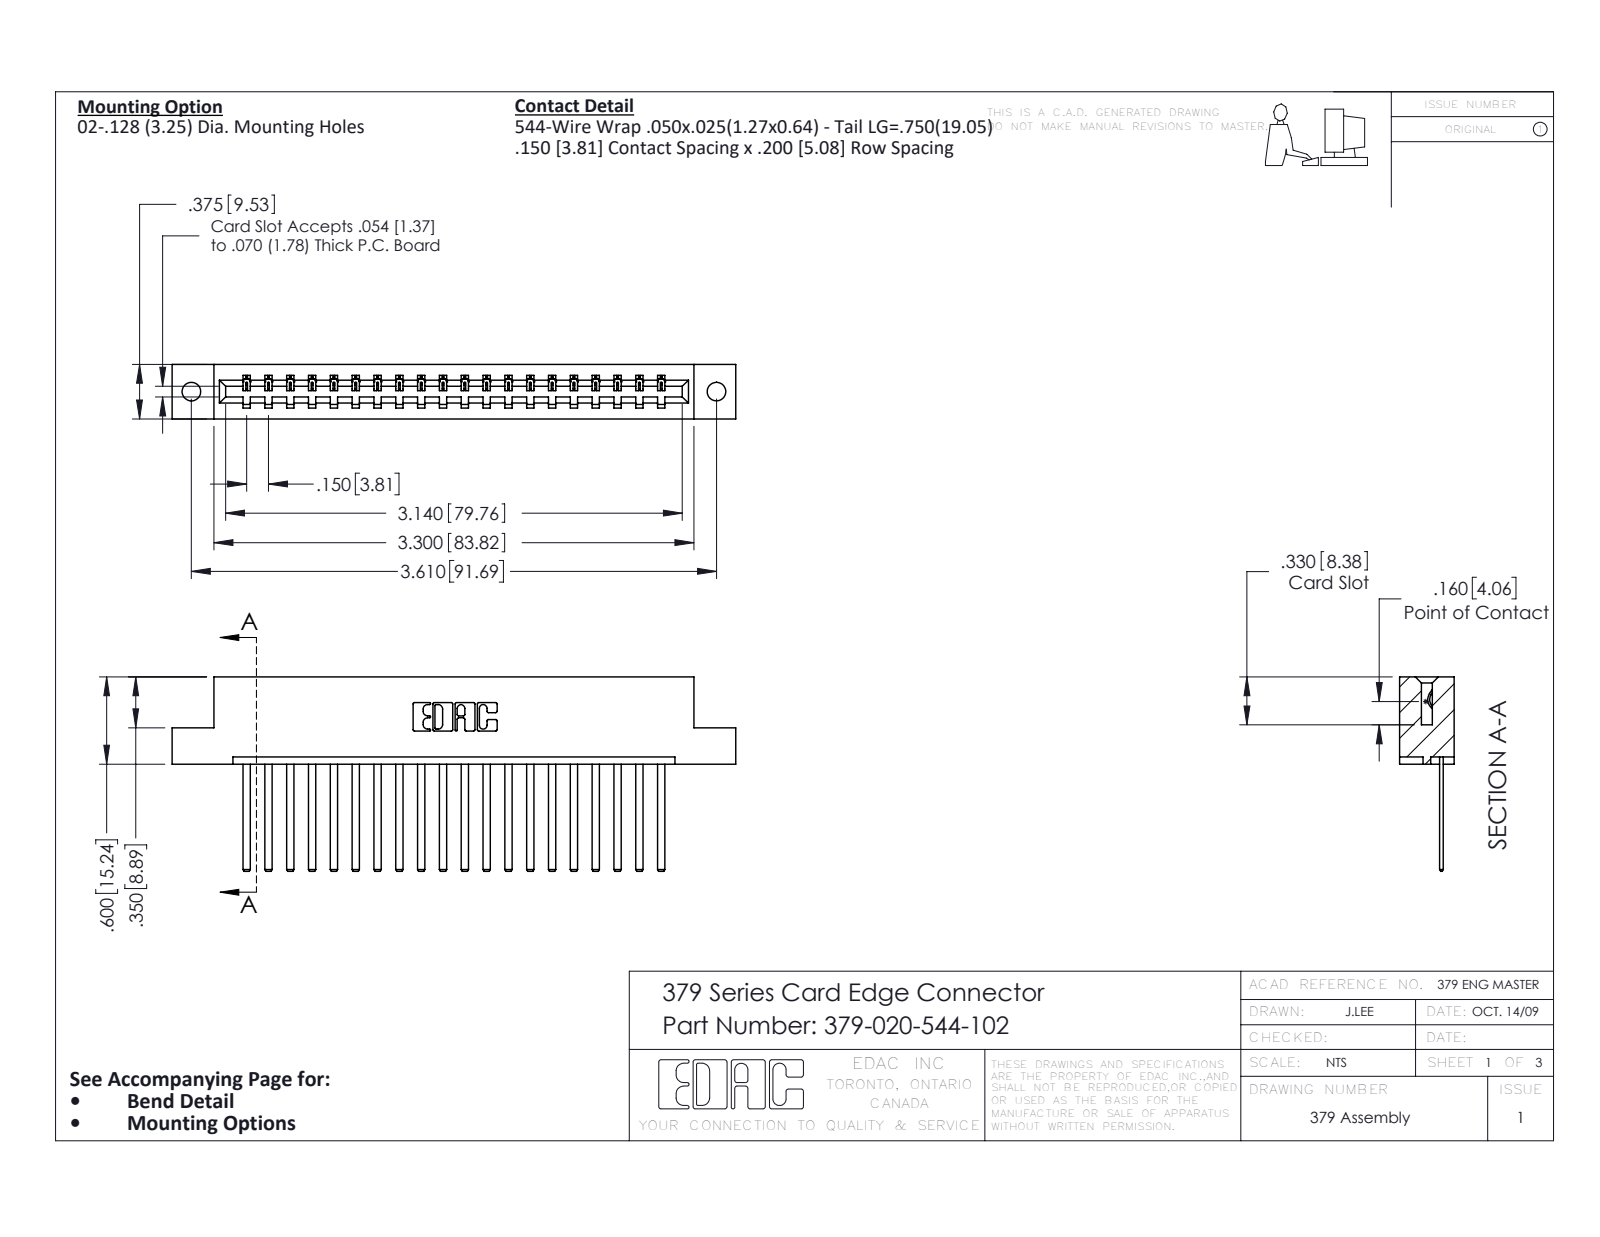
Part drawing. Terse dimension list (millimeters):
name: 379-020-544-102; 379 Part_Flush - .128 Dia; 345-292-001_345-293-144
written by: SolidWorks 2016 (CONFIG_CONTROL_DESIGN)
unit: mm
bodies: 21 solids, 1154 faces (830 planar, 324 cylindrical, 0 other)
size: 98.4 × 34 × 9.5
volume: 10 300 mm³; area: 10 900 mm²
holes: 2× ⌀3.3
rounds: 40× R0.2, 22× R0.3, 6× R0.2, 6× R0.8, 3× R0.7, 1× R0.4, 1× R0.6, 1× R0.6
face distances: 7.6, 1.9, 9.5, 15.2, 7, 2.5, 0.6, 3.8, 5.7, 11.4
hole spacings: 91.7
